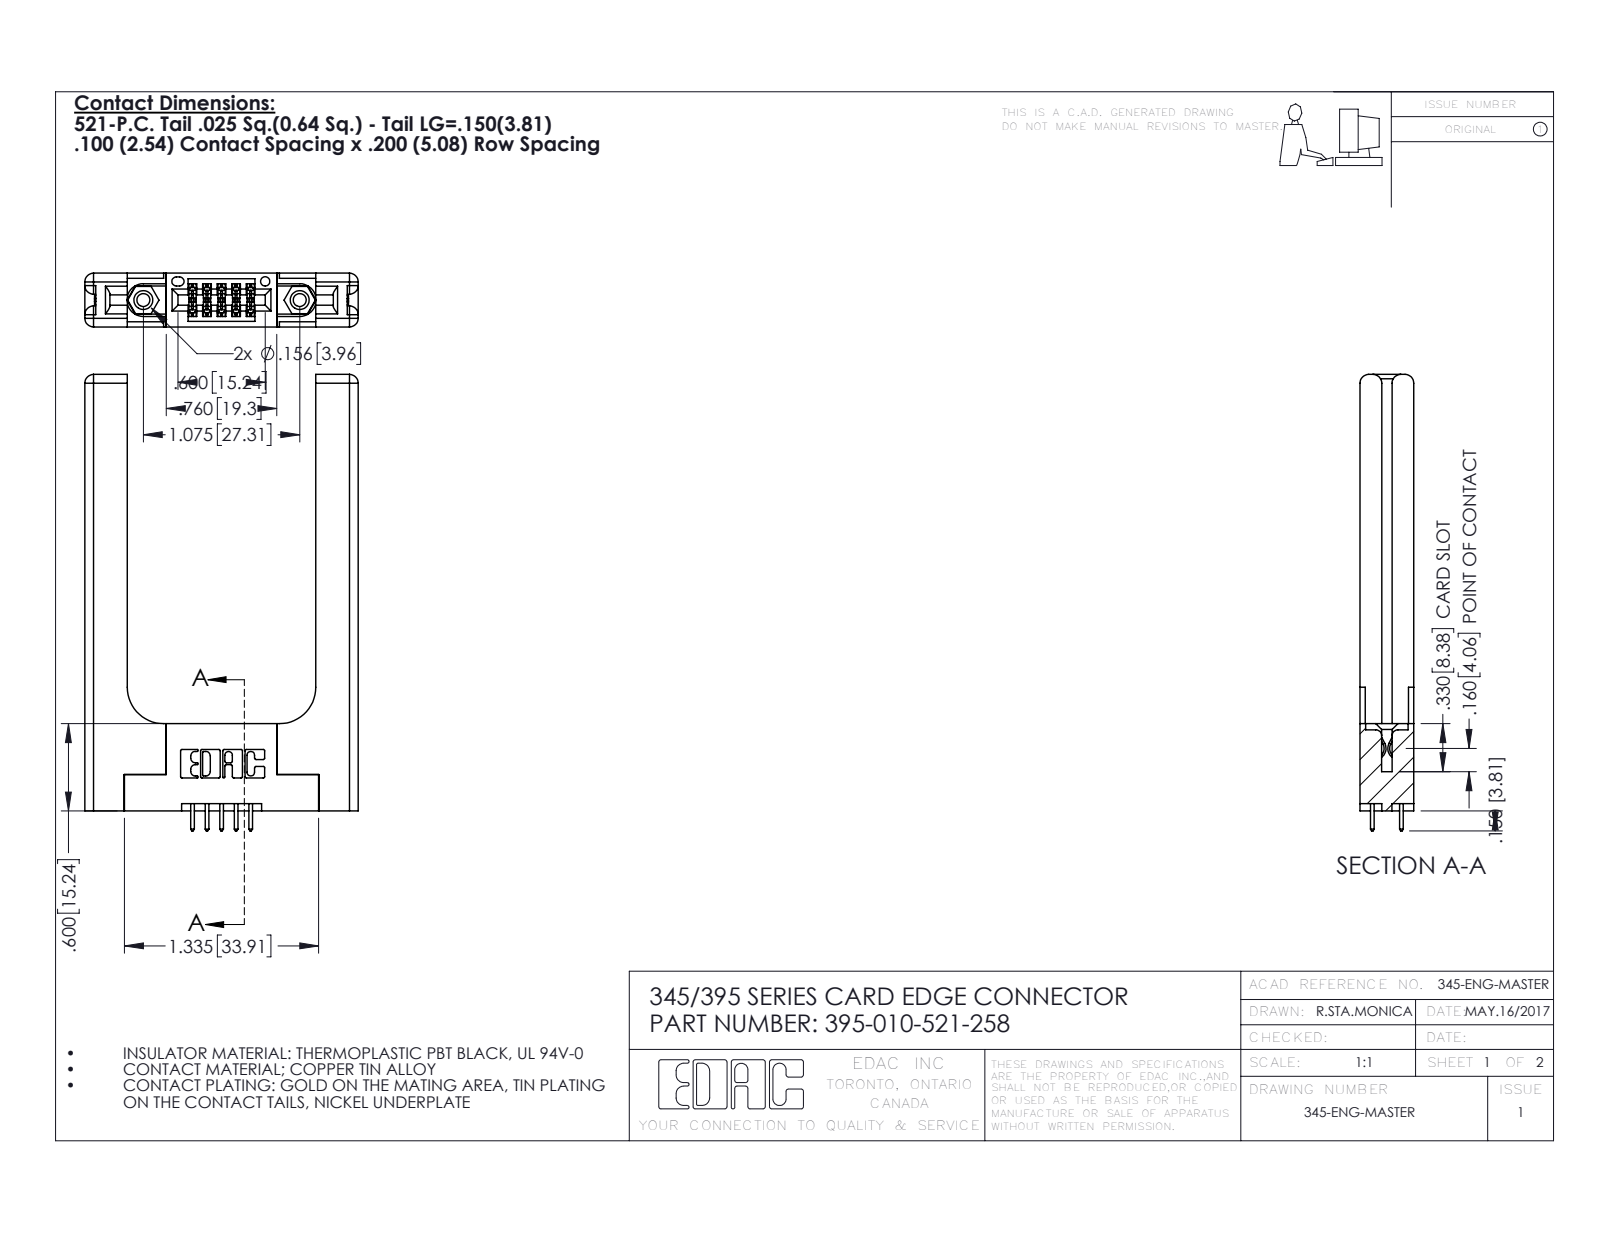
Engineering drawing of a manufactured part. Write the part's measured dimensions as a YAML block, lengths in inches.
part_name: "345-250-001_345-250-001-102; 345 Part_Flush Mounting Lugs - 0.156 Dia-TH; 345-292-001_345-293-121; 345-220-058_345-220-058 (+1 more)"
step_written_by: "SolidWorks 2016 (CONFIG_CONTROL_DESIGN)"
units: inches
bodies: {solids: 15, faces: 882, planar: 558, cylindrical: 264, other: 60}
overall_size: [3.137, 1.879, 0.37]
volume: 0.779
surface_area: 16.52
round_holes:
  - {diameter: 0.089, count: 2}
  - {diameter: 0.125, count: 2}
  - {diameter: 0.156, count: 2}
  - {diameter: 0.064, count: 1}
round_bosses_or_shafts:
  - {diameter: 0.155, count: 2}
partial_cylinders:
  - {radius: 0.01, count: 22}
  - {radius: 0.06, count: 16}
  - {radius: 0.006, count: 15}
  - {radius: 0.01, count: 10}
  - {radius: 0.007, count: 6}
  - {radius: 0.031, count: 6}
  - {radius: 0.026, count: 3}
  - {radius: 0.014, count: 2}
face_to_face_distances: [0.37, 0.15, 0.22, 0.072, 1.296, 0.077, 0.148, 0.298, 0.071, 0.2]
hole_center_spacings: [0.27, 0.847, 1.075]
